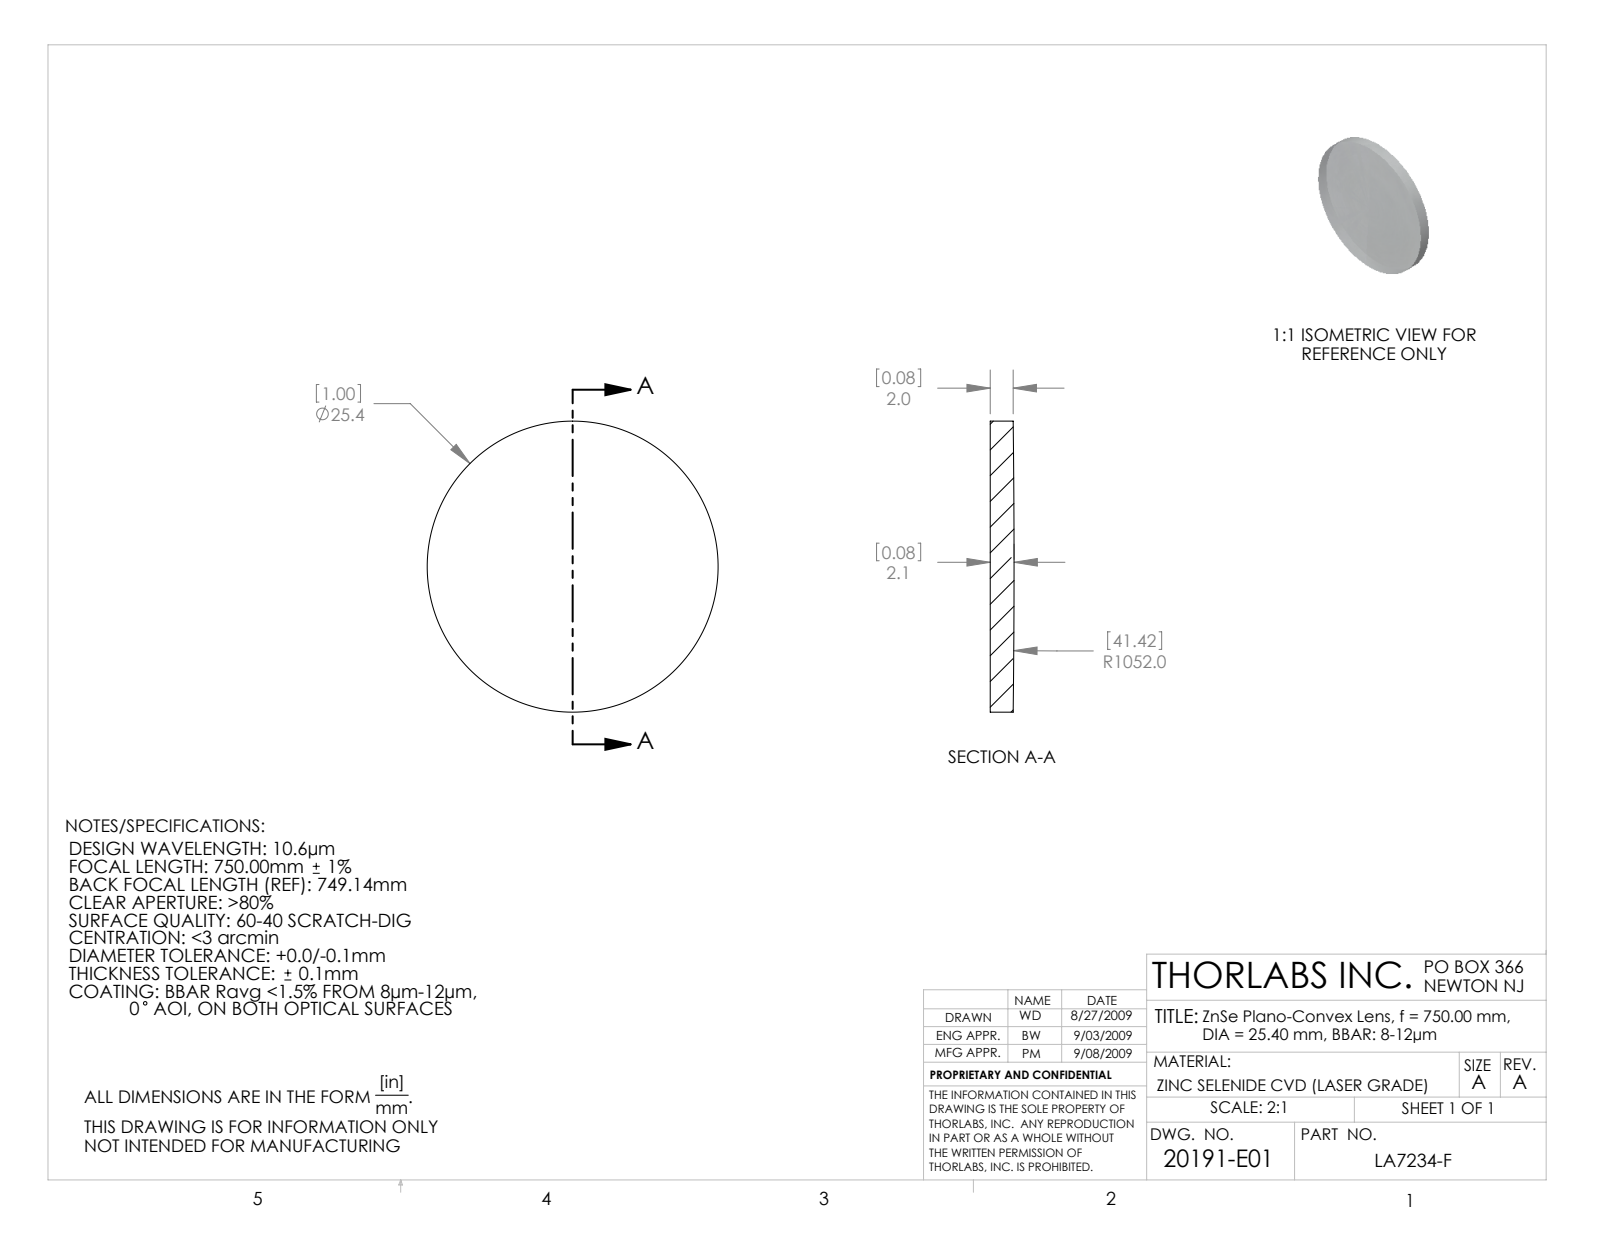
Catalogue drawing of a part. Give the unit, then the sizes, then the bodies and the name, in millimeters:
Units: millimetres
Overall size (bounding box): 25.4 × 25.4 × 2.08
Round bosses / shafts (diameter × count): ⌀25.4 ×1
Volume: 1 035 mm³ · Surface area: 1 173 mm²
Bodies: 1 solid, 5 faces (1 planar, 2 cylindrical, 2 other)
Part name (STEP PRODUCT): 20191-E0W
STEP written by: SolidWorks 2007 (CONFIG_CONTROL_DESIGN)
